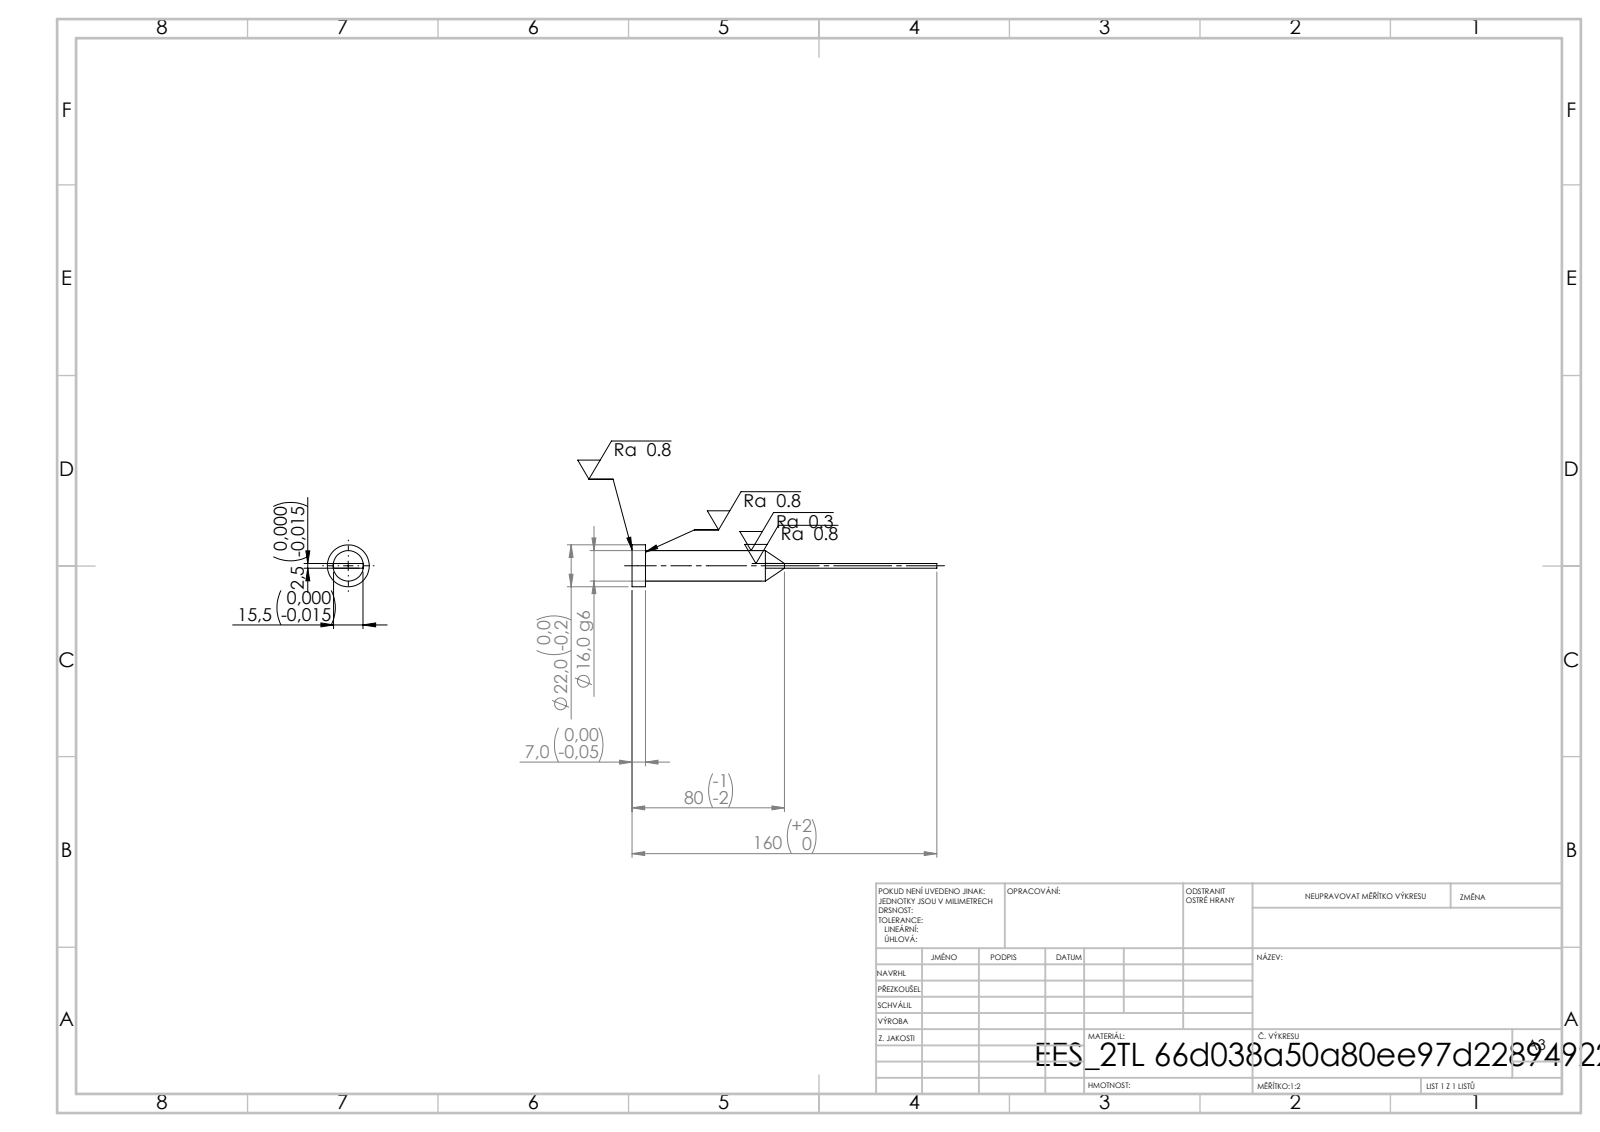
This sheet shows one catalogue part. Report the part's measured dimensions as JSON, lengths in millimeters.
{"step_written_by": "SolidWorks 2019 (CONFIG_CONTROL_DESIGN)", "units": "millimeters", "bodies": {"solids": 1, "faces": 15, "planar": 7, "cylindrical": 4, "other": 4}, "overall_size": [160, 22, 22], "volume_mm3": 19565, "surface_area_mm2": 7579, "round_bosses_or_shafts": [[22, 1], [16, 1]], "face_to_face_distances": [2.5, 15.5, 7, 160, 153]}
